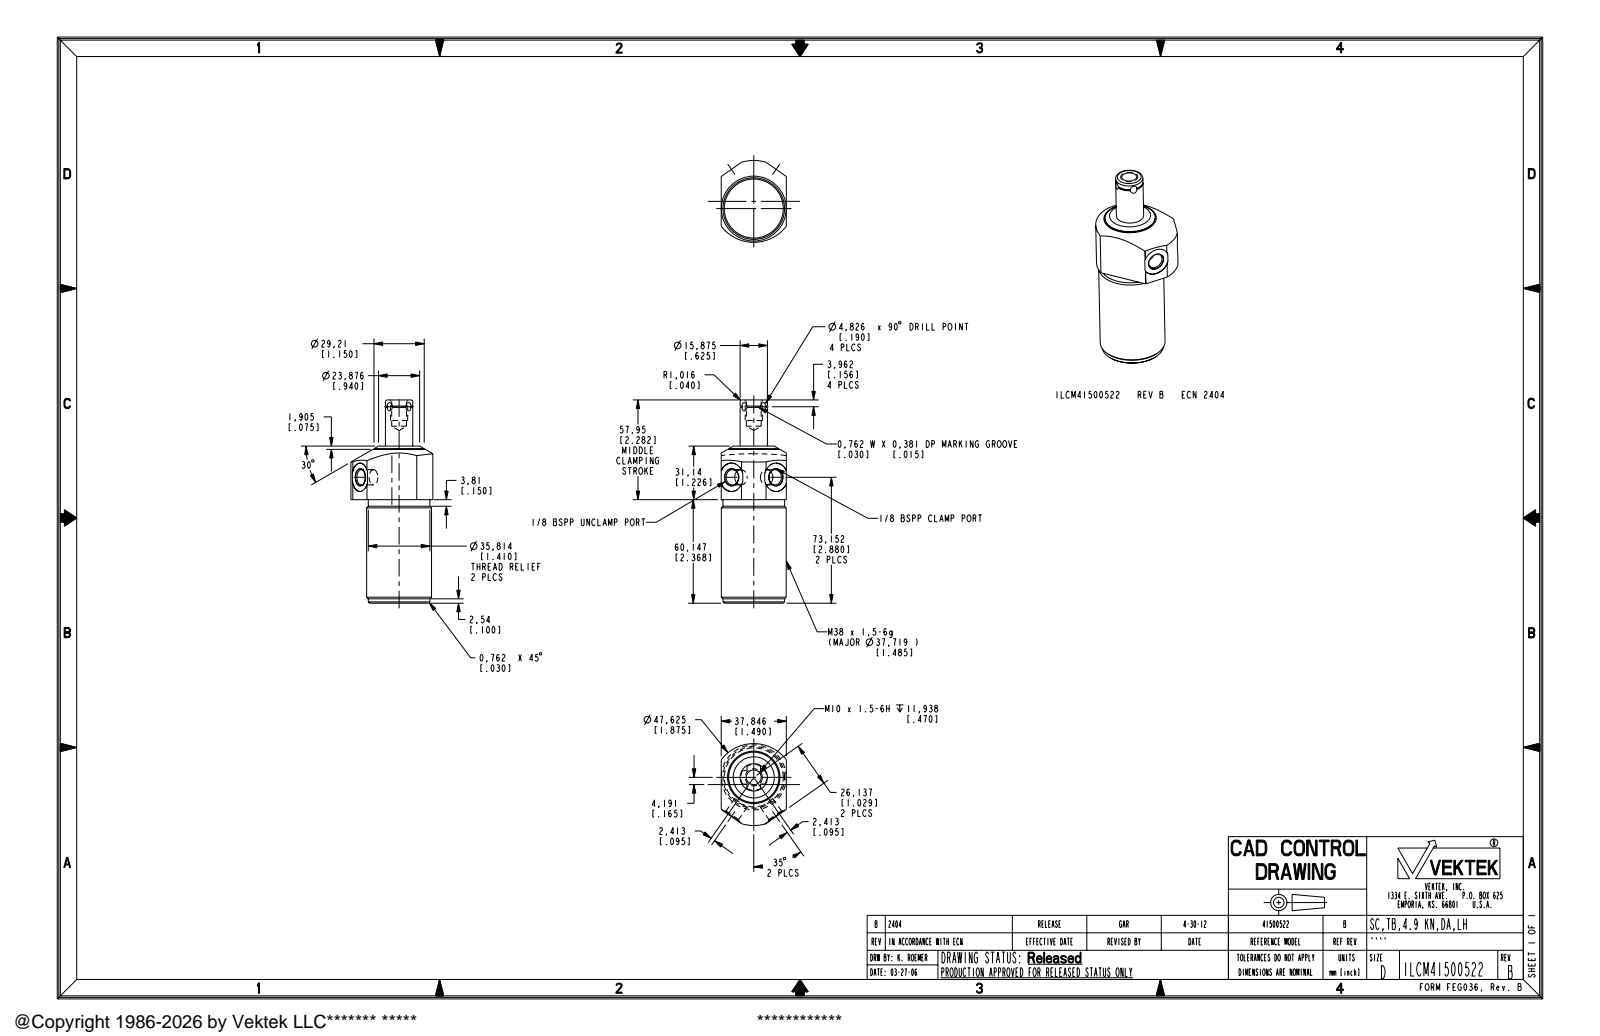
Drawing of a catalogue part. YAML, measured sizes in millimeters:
part_name: "ILCM41500522"
step_written_by: "PRO/ENGINEER BY PARAMETRIC TECHNOLOGY CORPORATION, 2007460 (AUTOMOTIVE_DESIGN_CC2)"
units: millimeters
bodies: {solids: 1, faces: 88, planar: 24, cylindrical: 38, other: 26}
overall_size: [118.1, 47.62, 37.85]
volume: 114068
surface_area: 16778
round_holes:
  - {diameter: 8.84, count: 2}
  - {diameter: 10.03, count: 2}
  - {diameter: 8.61, count: 1}
round_bosses_or_shafts:
  - {diameter: 37.72, count: 1}
  - {diameter: 35.81, count: 1}
  - {diameter: 29.21, count: 1}
  - {diameter: 15.88, count: 1}
  - {diameter: 10.01, count: 1}
partial_cylinders:
  - {radius: 8.26, count: 2}
  - {radius: 7.56, count: 1}
  - {radius: 23.81, count: 1}
face_to_face_distances: [37.84, 60.15, 91.29, 31.14, 9.4, 118.1, 57.95, 26.81, 9.66, 9.65]
